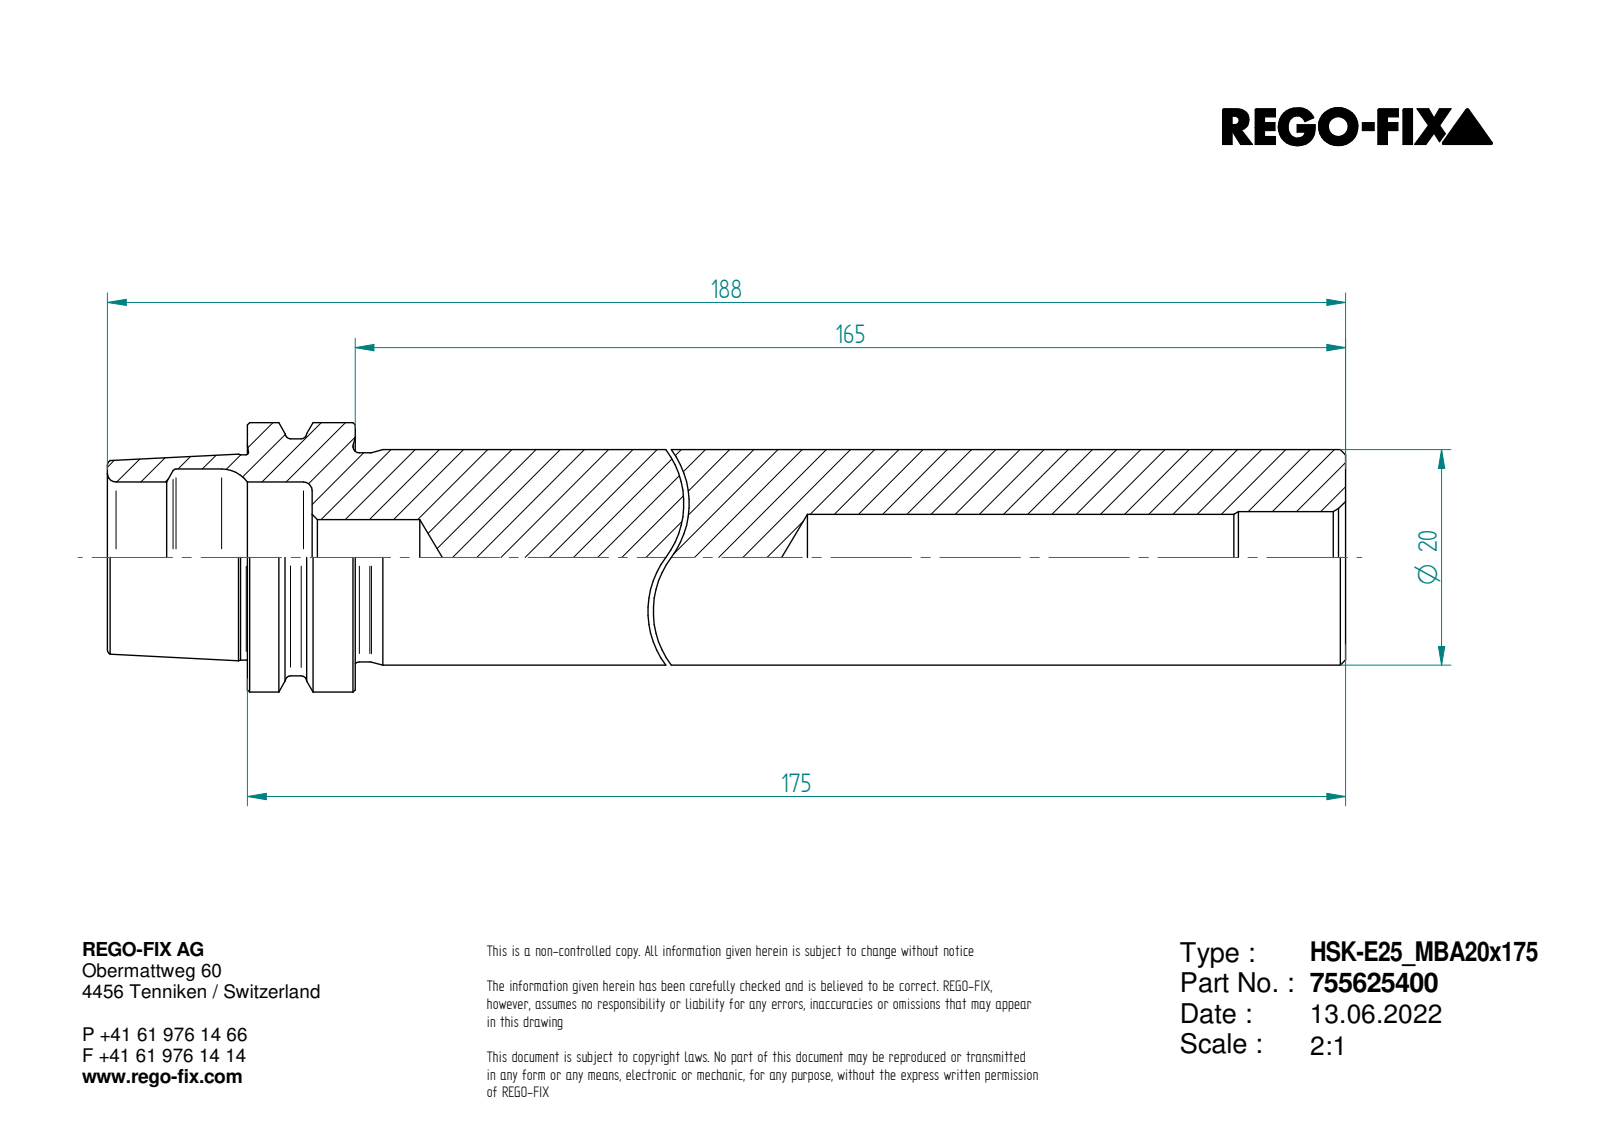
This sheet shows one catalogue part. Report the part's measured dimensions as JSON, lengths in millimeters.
{"part_name": "0026159", "step_written_by": "ST-DEVELOPER v16.7 (AUTOMOTIVE_DESIGN)", "units": "millimeters", "bodies": {"solids": 1, "faces": 44, "planar": 5, "cylindrical": 12, "other": 27}, "overall_size": [188, 25, 25], "volume_mm3": 53618, "surface_area_mm2": 15322, "round_holes": [[7, 1], [8, 1], [8.5, 1], [14, 1], [16.4, 1]], "round_bosses_or_shafts": [[25, 1], [22, 1], [20, 1], [19.4, 1], [19.06, 1]], "face_to_face_distances": [175, 10, 165, 6, 4, 169, 13, 19, 23, 188]}
